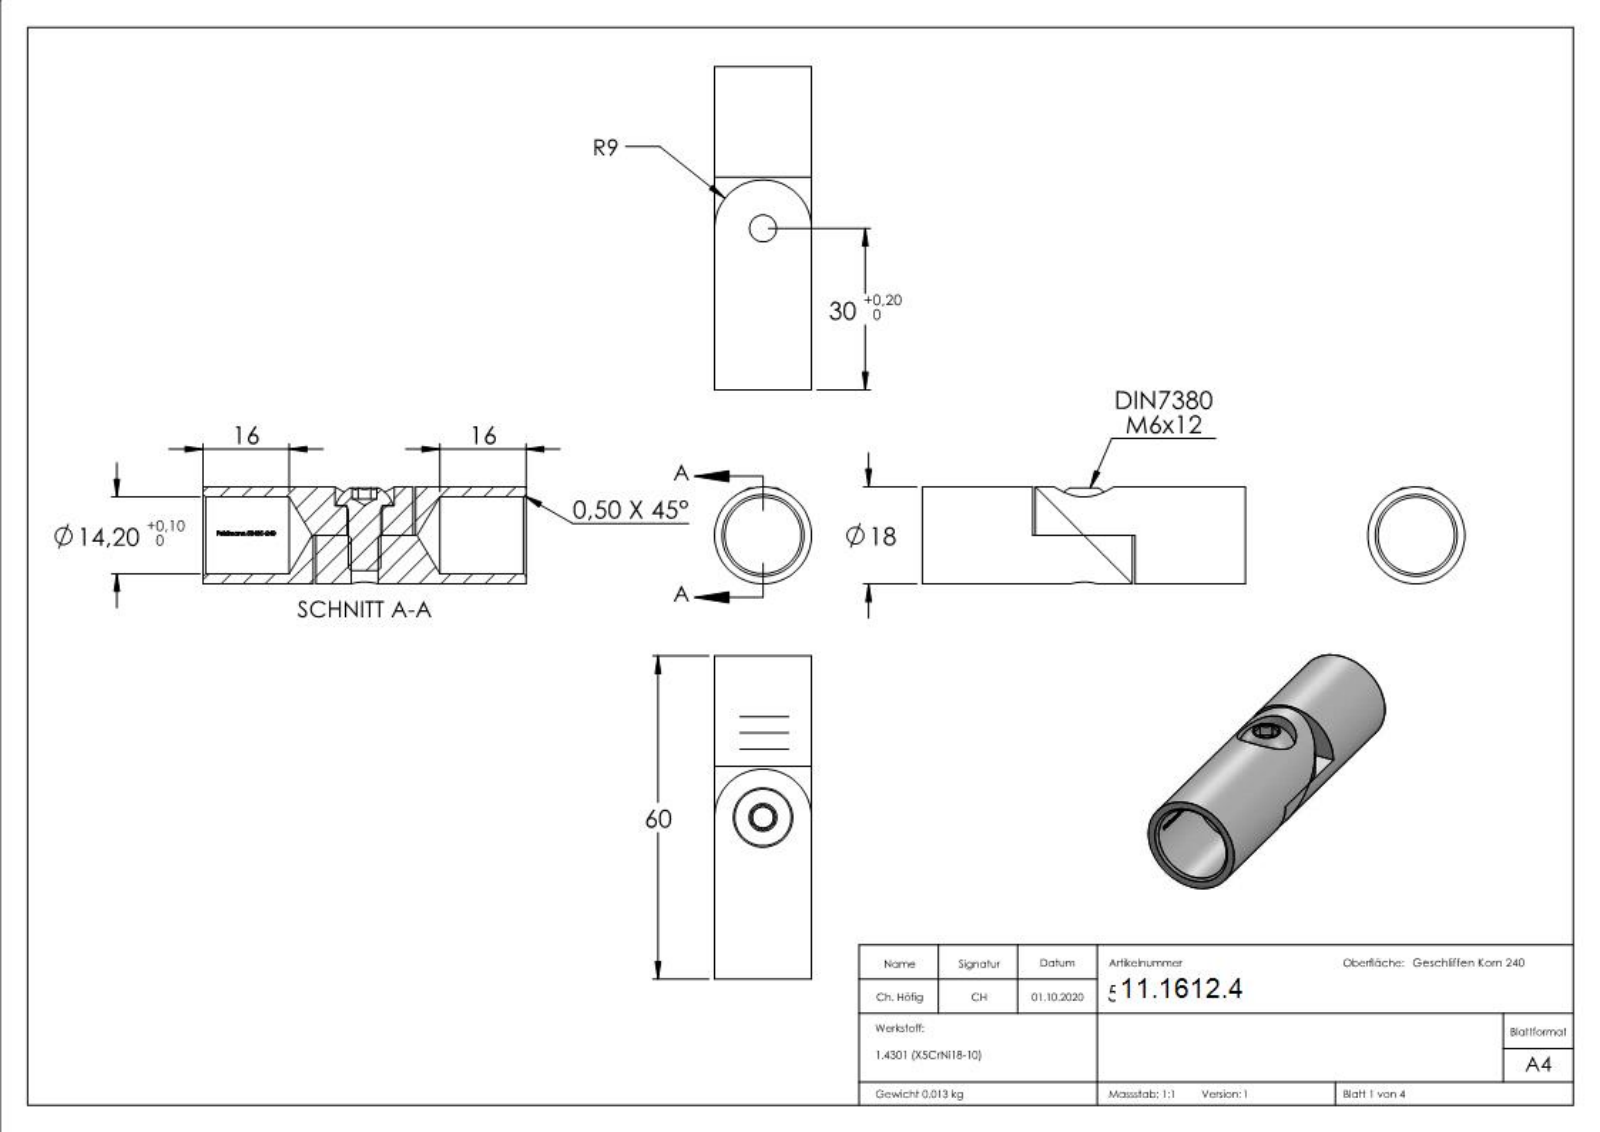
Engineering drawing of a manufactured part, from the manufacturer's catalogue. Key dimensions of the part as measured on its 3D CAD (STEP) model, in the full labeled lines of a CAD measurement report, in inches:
Part name (STEP PRODUCT): 50431-240; 504XX-240 Teil1_50431-240 Teil1; DIN 7380; 504XX-240 Teil1 (+3 more)
STEP written by: SolidWorks 2018 (CONFIG_CONTROL_DESIGN)
Units: inches
Bodies: 3 solids, 287 faces (122 planar, 46 cylindrical, 119 other)
Overall size (bounding box): 2.362 × 0.709 × 0.709
Volume: 0.557 in³ · Surface area: 10.87 in²
Round holes (diameter × count): ⌀0.197 ×1, ⌀0.256 ×1, ⌀0.433 ×1, ⌀0.559 ×1
Round bosses / shafts (diameter × count): ⌀0.709 ×2, ⌀0.413 ×1, ⌀0.236 ×1
Partial cylindrical surfaces — rounded edges, fillets, slot ends (radius × count): R0.283 ×1
Main face-to-face distances: 0.807, 1.555, 0.748, 0.217, 2.362, 0.256, 0.472, 0.157, 0.602, 0.346
